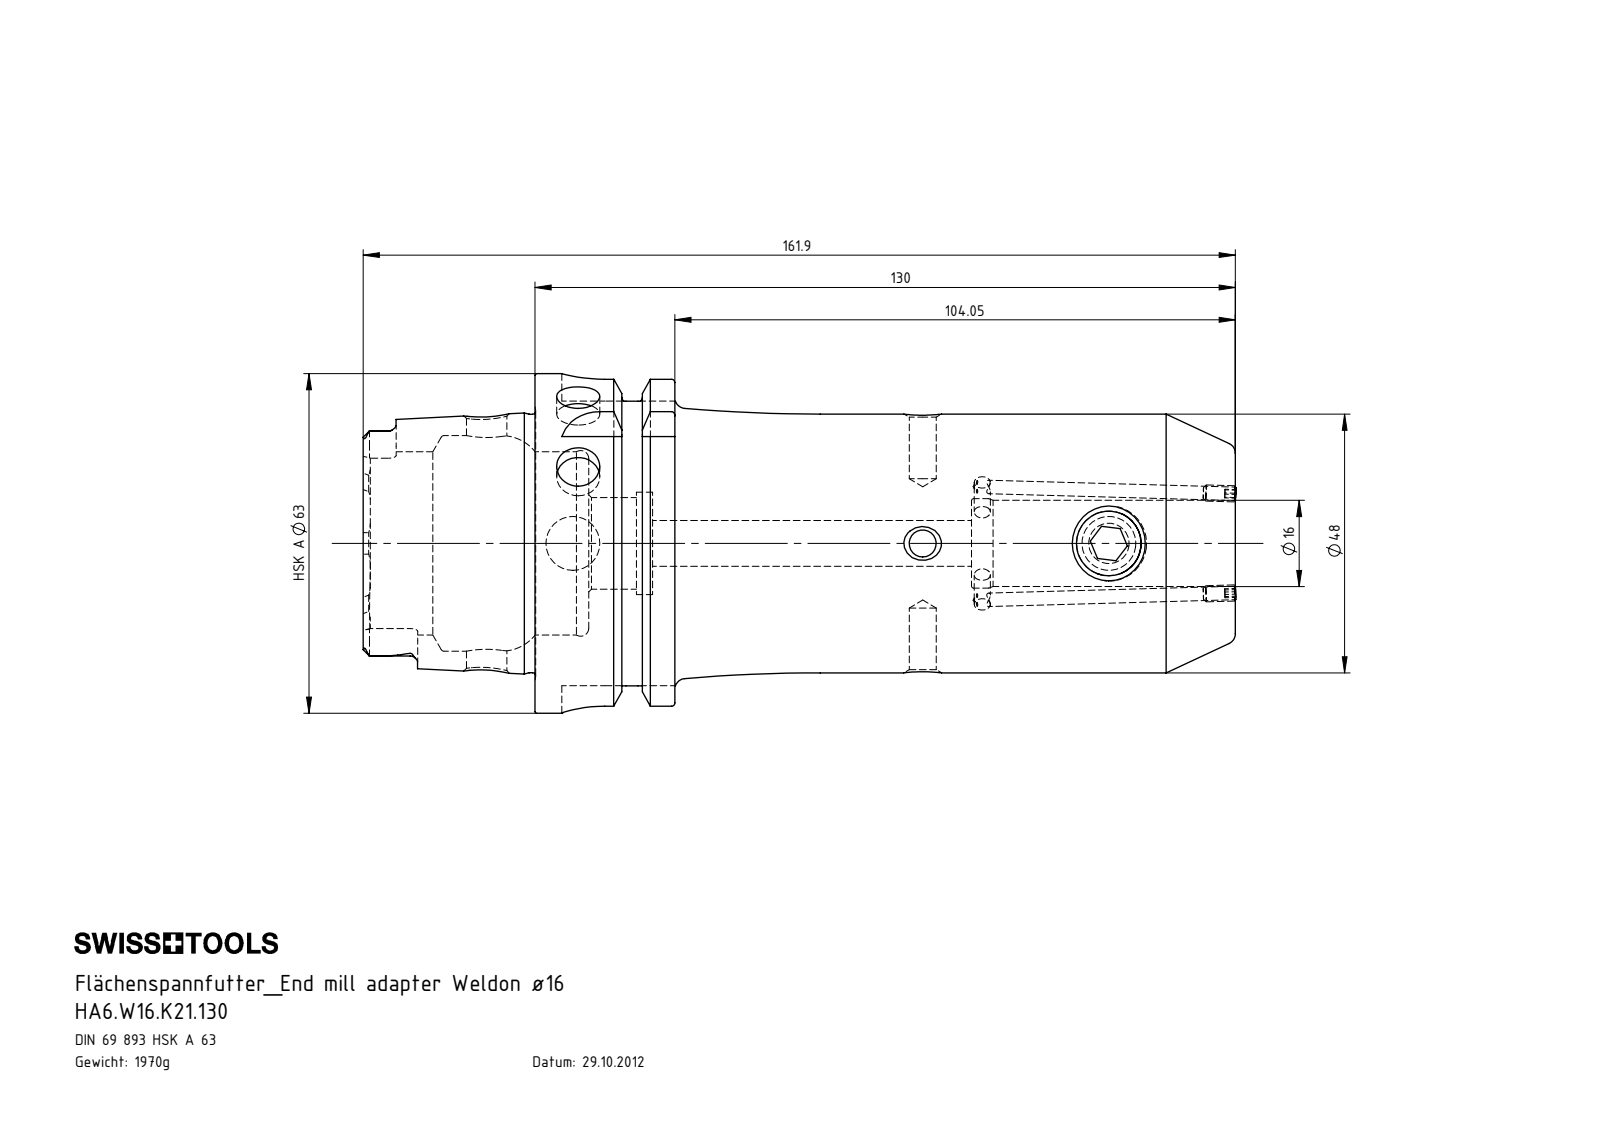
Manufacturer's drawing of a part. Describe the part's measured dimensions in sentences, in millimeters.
The part is named "HA6-W16.K21.130; ERU-CJ2.001.006; W16-ER1.001.016; HA6-W16.K21.130_A_Fertigbearbeitung". Its 3-D file was written by "SolidWorks 2012 (CONFIG_CONTROL_DESIGN)". It is 4 solids with 290 faces: 78 planar, 82 cylindrical and 130 other. Overall it measures 161.98 by 63 by 63 millimeters. Its volume is 250 901 cubic millimeters and its surface area 44 265 square millimeters. Round holes: 2 of diameter 2.5, 2 of diameter 5, 2 of diameter 8, 1 of diameter 3, 1 of diameter 7.5, 1 of diameter 8.5, 1 of diameter 10, 1 of diameter 12, 1 of diameter 16, 1 of diameter 16.6, 1 of diameter 17, 1 of diameter 19. Round bosses or shafts: 2 of diameter 3, 1 of diameter 63, 1 of diameter 54.95, 1 of diameter 48, 1 of diameter 47.94, 1 of diameter 14. Partial cylindrical surfaces (rounded edges, fillets, slot ends): 6 of radius 1.4, 4 of radius 2.88, 4 of radius 8. The main face-to-face distances are 130, 25.95, 104.05, 16, 9.95, 120.05, 31.9, 41.85, 57.85, 161.9. The hole center spacings are 34.55, 64.95, 80.95, 99.5.
